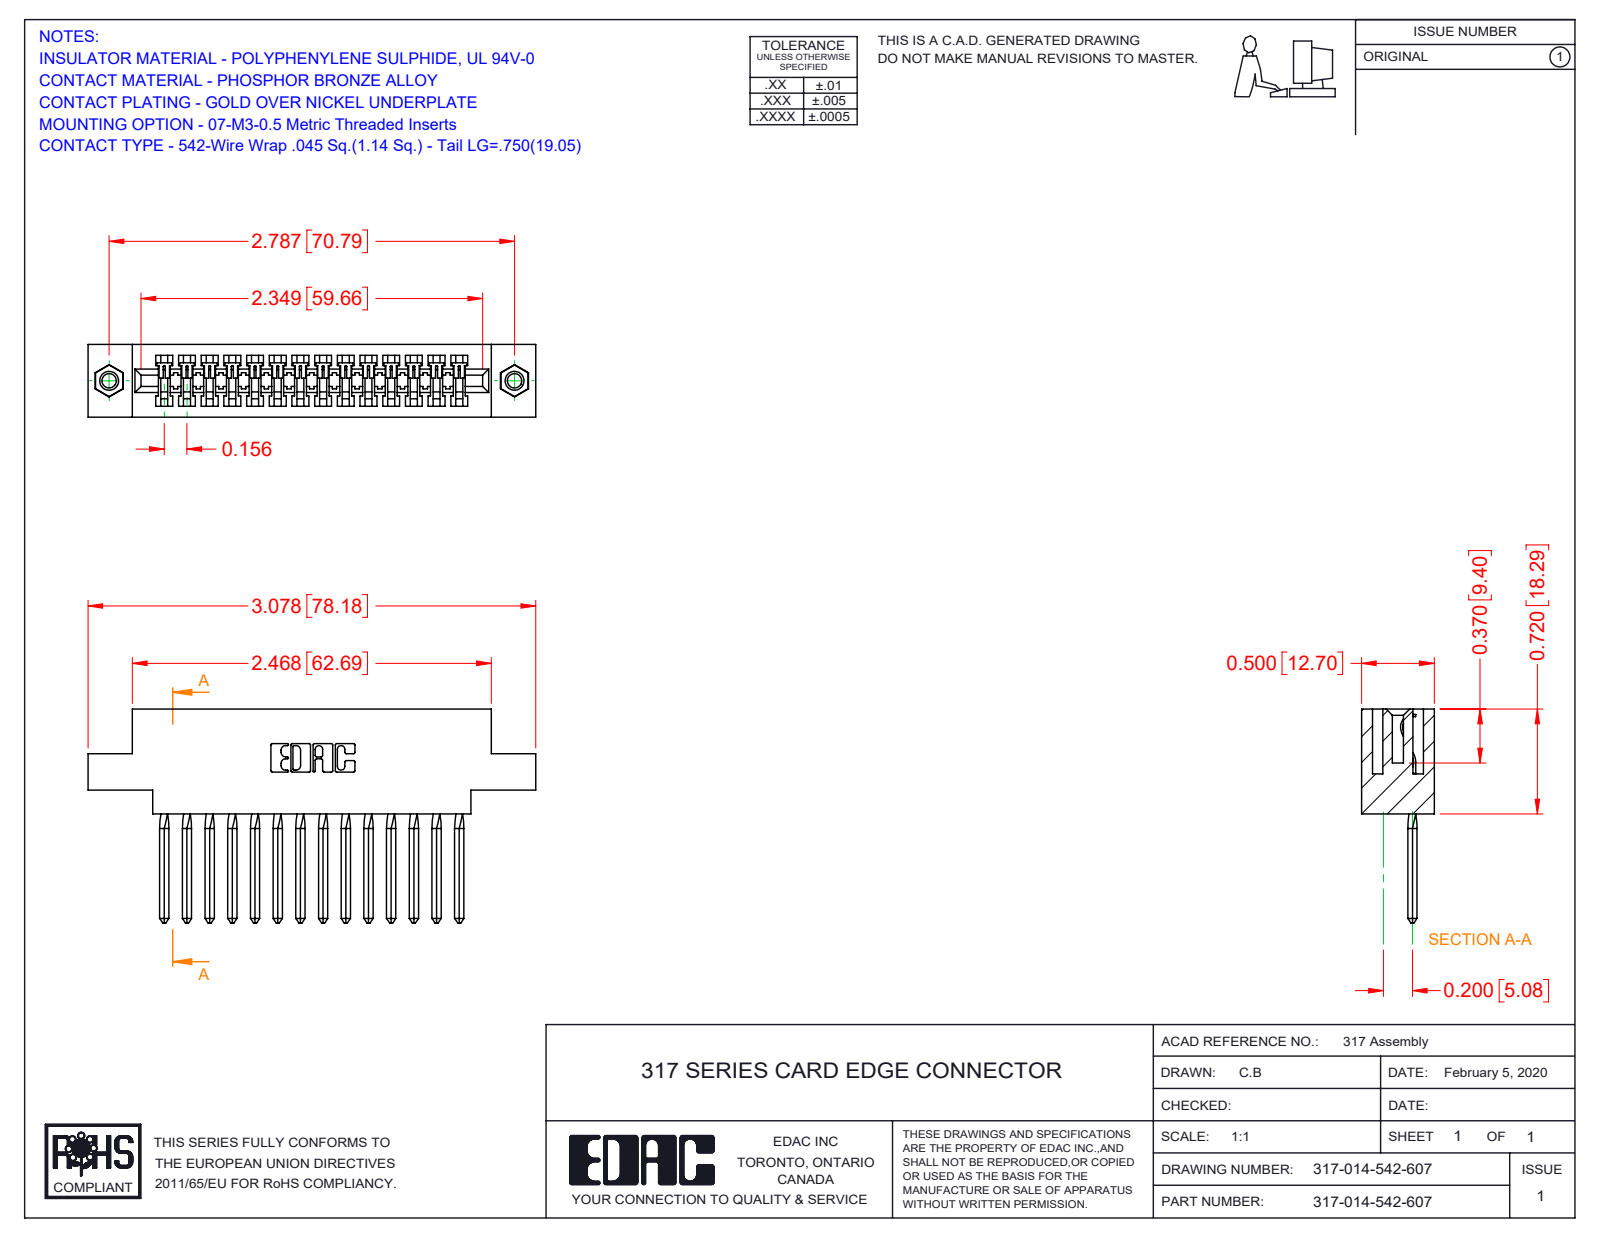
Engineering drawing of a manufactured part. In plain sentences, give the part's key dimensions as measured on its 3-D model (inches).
The part is named "317-014-542-607; 317 Part_.156 Dia - TI; 345-250-001_345-250-005-103; 317-290-003_542". Its 3-D file was written by "SolidWorks 2016 (CONFIG_CONTROL_DESIGN)". It is 17 solids with 1212 faces: 986 planar, 154 cylindrical and 72 other. Overall it measures 3.078 by 1.47 by 0.5 inches. Its volume is 0.691 cubic inches and its surface area 20.48 square inches. Round holes: 2 of diameter 0.098, 2 of diameter 0.125, 2 of diameter 0.156. Round bosses or shafts: 2 of diameter 0.155. Partial cylindrical surfaces (rounded edges, fillets, slot ends): 28 of radius 0.006, 22 of radius 0.01, 6 of radius 0.007, 6 of radius 0.031, 3 of radius 0.026, 1 of radius 0.074, 1 of radius 0.089, 1 of radius 0.1. The main face-to-face distances are 0.5, 0.075, 0.425, 0.11, 0.35, 0.065, 0.22, 0.136, 0.72, 0.116. The hole center spacings are 2.787.
